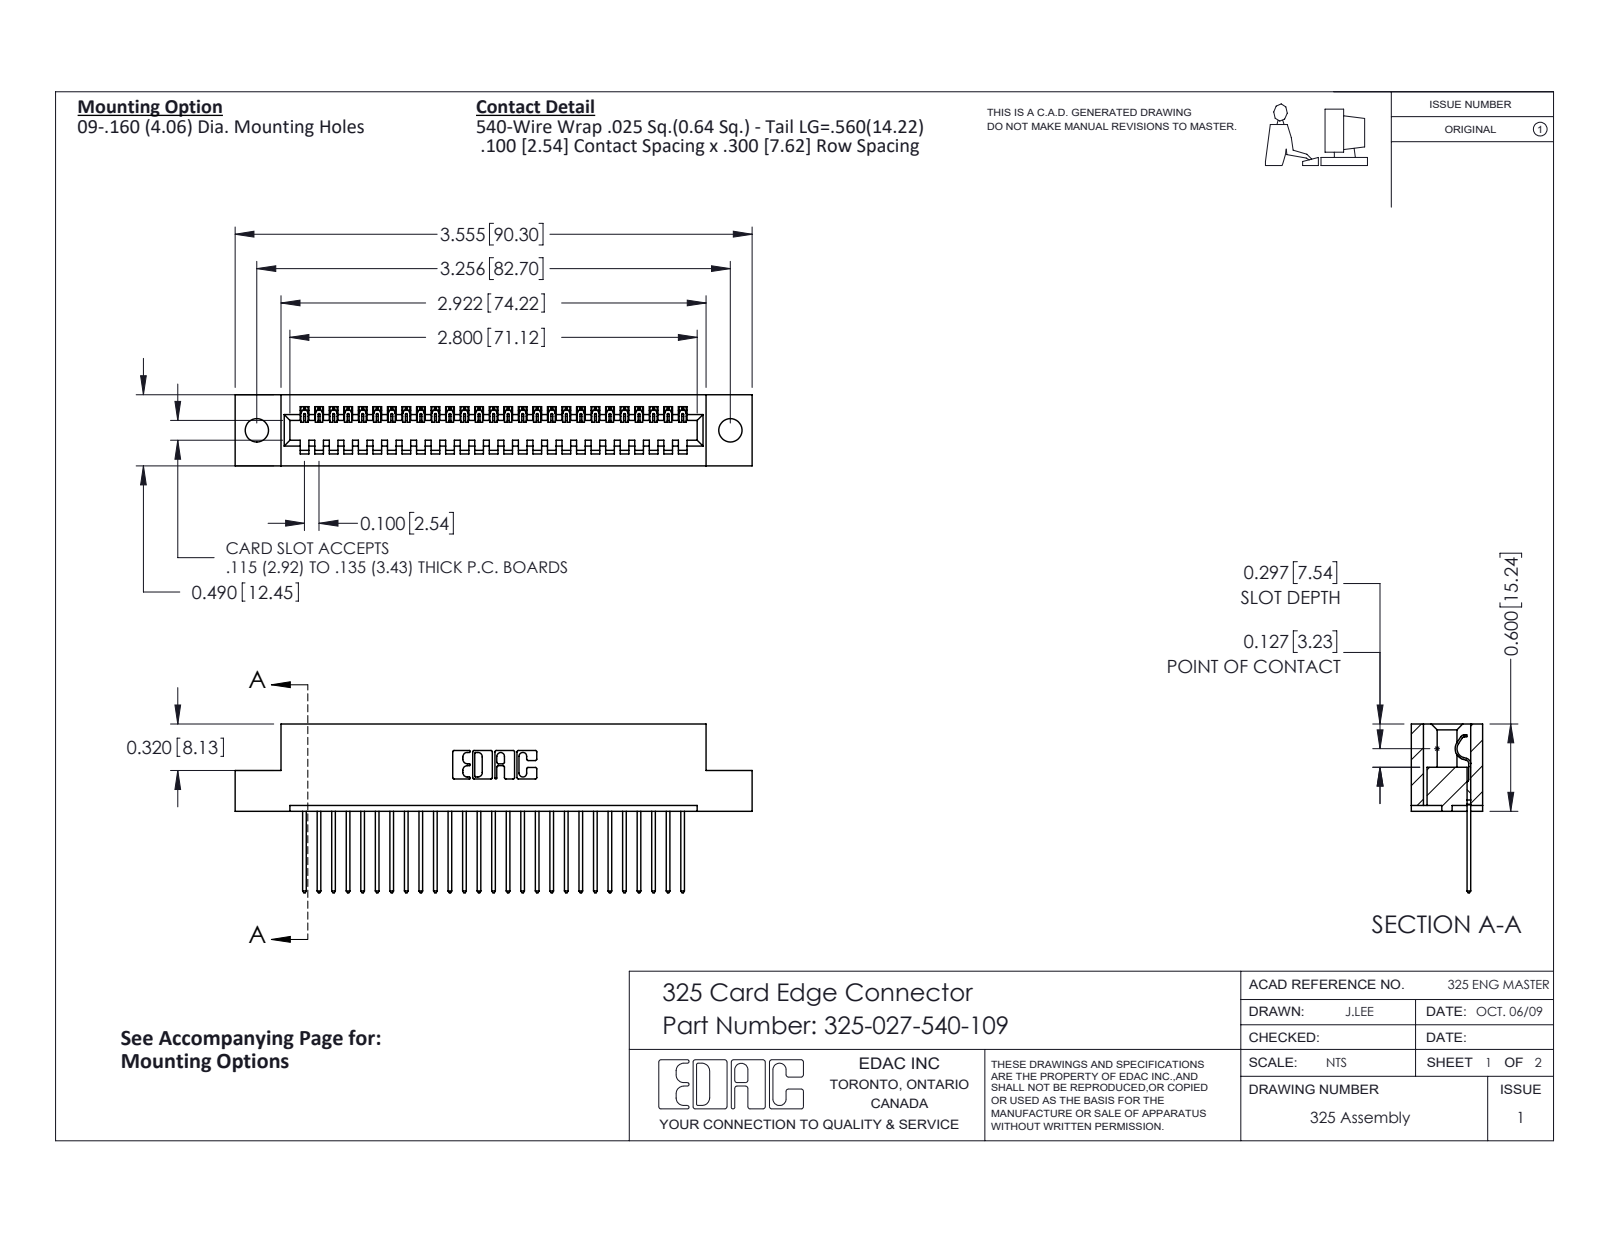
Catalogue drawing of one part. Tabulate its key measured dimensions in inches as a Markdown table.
| quantity | value |
| --- | --- |
| part name | 325-292-001_325-293-140; 325 Part_.160 TH; 325-027-540-109 |
| STEP written by | SolidWorks 2016 (CONFIG_CONTROL_DESIGN) |
| units | inches |
| bodies | 28 solids, 1680 faces (1204 planar, 476 cylindrical, 0 other) |
| overall size | 3.555 × 1.16 × 0.49 |
| volume | 0.68 in³ |
| surface area | 18.75 in² |
| round holes (diameter × count) | 0.16 × 2 |
| partial cylindrical surfaces (radius × count) | 0.006 × 54, 0.01 × 54, 0.01 × 22, 0.007 × 6, 0.031 × 6, 0.026 × 3, 0.014 × 1, 0.022 × 1 |
| main face-to-face distances | 0.083, 0.407, 0.3, 0.49, 0.107, 0.383, 0.025, 0.04, 0.325, 0.1 |
| hole center spacings | 3.256 |
